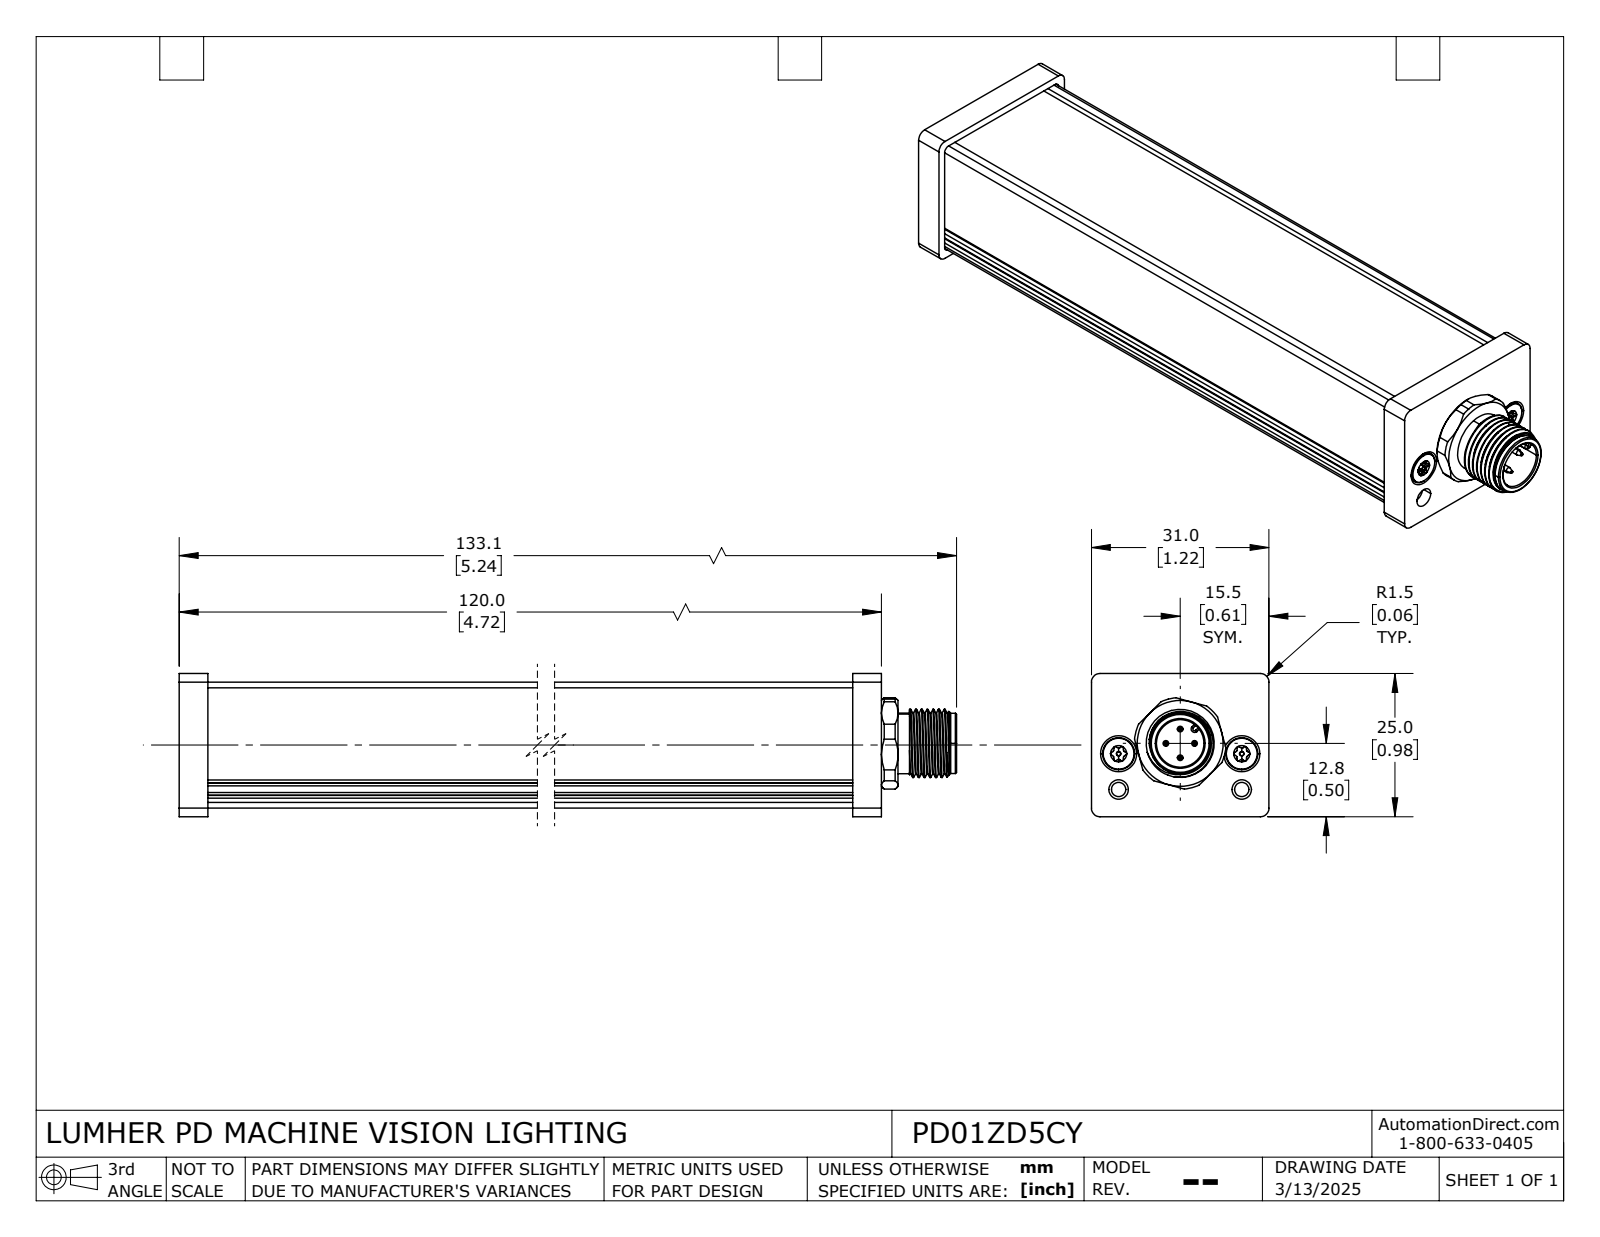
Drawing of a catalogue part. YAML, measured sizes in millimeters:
part_name: "PD01__5_Y"
step_written_by: "SolidWorks 2024 (AUTOMOTIVE_DESIGN)"
units: millimeters
bodies: {solids: 1, faces: 563, planar: 89, cylindrical: 296, other: 178}
overall_size: [133.1, 31, 25]
volume: 72118
surface_area: 21386
round_holes:
  - {diameter: 1.45, count: 4}
  - {diameter: 3.4, count: 4}
  - {diameter: 2.5, count: 2}
  - {diameter: 8.3, count: 1}
  - {diameter: 9.4, count: 1}
round_bosses_or_shafts:
  - {diameter: 1.4, count: 4}
  - {diameter: 1, count: 4}
  - {diameter: 5.6, count: 2}
  - {diameter: 3, count: 2}
  - {diameter: 0.8, count: 2}
  - {diameter: 11.9, count: 1}
  - {diameter: 10.6, count: 1}
  - {diameter: 10.5, count: 1}
partial_cylinders:
  - {radius: 0.57, count: 24}
  - {radius: 0.25, count: 12}
  - {radius: 0.5, count: 8}
  - {radius: 1, count: 8}
  - {radius: 3, count: 6}
  - {radius: 1.5, count: 4}
  - {radius: 0.3, count: 2}
  - {radius: 1.02, count: 2}
face_to_face_distances: [28, 2, 3, 1.5, 1, 115, 118, 117, 1.4, 23.5]
hole_center_spacings: [2.5, 3.54, 5, 6.25, 8.44, 10.77, 10.9, 11.53]
